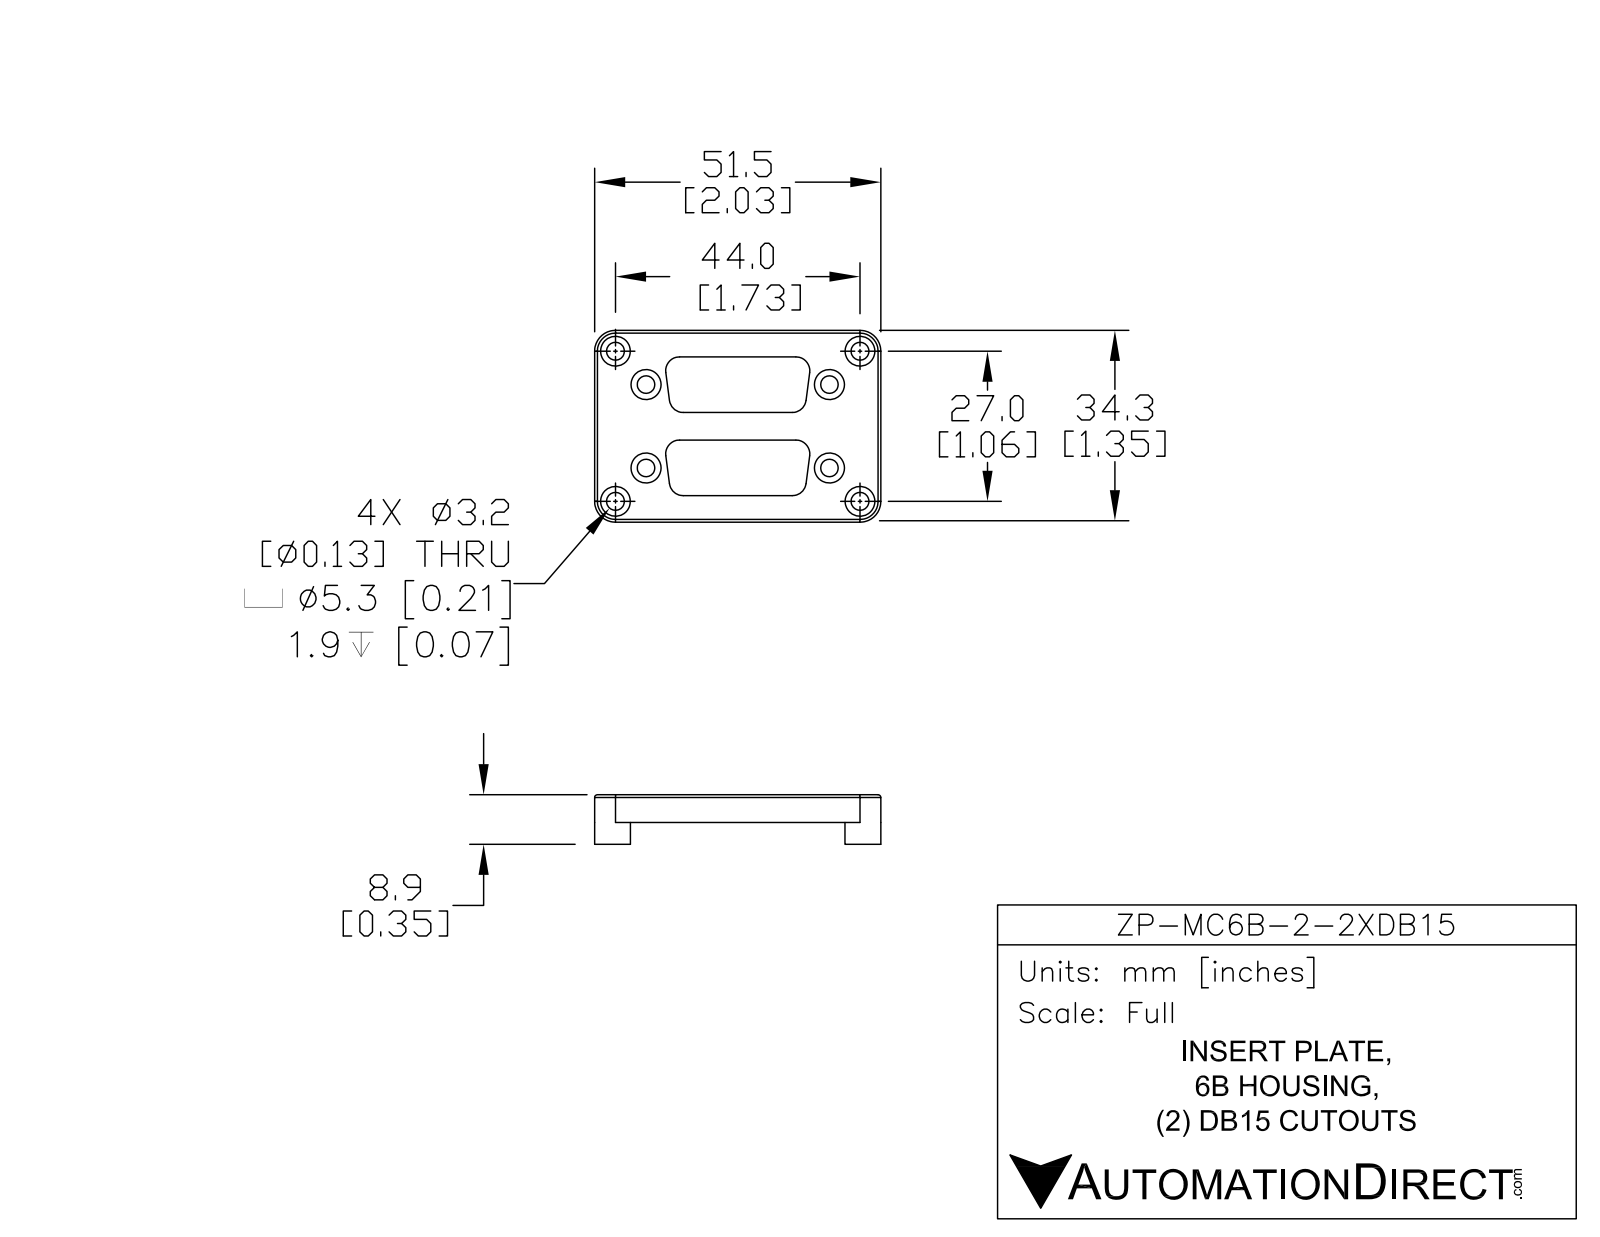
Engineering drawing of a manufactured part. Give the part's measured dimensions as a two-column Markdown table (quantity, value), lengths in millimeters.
| quantity | value |
| --- | --- |
| part name | ZP-MC6B-2-2XDB15 |
| STEP written by | SolidWorks 2014 (AUTOMOTIVE_DESIGN) |
| units | millimeters |
| bodies | 1 solid, 108 faces (50 planar, 46 cylindrical, 12 other) |
| overall size | 51.5 × 34.5 × 8.91 |
| volume | 4 148 mm³ |
| surface area | 4 767 mm² |
| round holes (diameter × count) | 3.15 × 4, 3.21 × 4, 5.35 × 4 |
| partial cylindrical surfaces (radius × count) | 2.5 × 8, 0.5 × 4, 3.75 × 4 |
| main face-to-face distances | 2.4, 2.15, 2.85, 5, 2.6, 32.1, 34.5, 27.9, 6.45, 45.05 |
| hole center spacings | 8.14, 21.71, 38.96, 43.85, 15, 27, 33, 36.25 |
